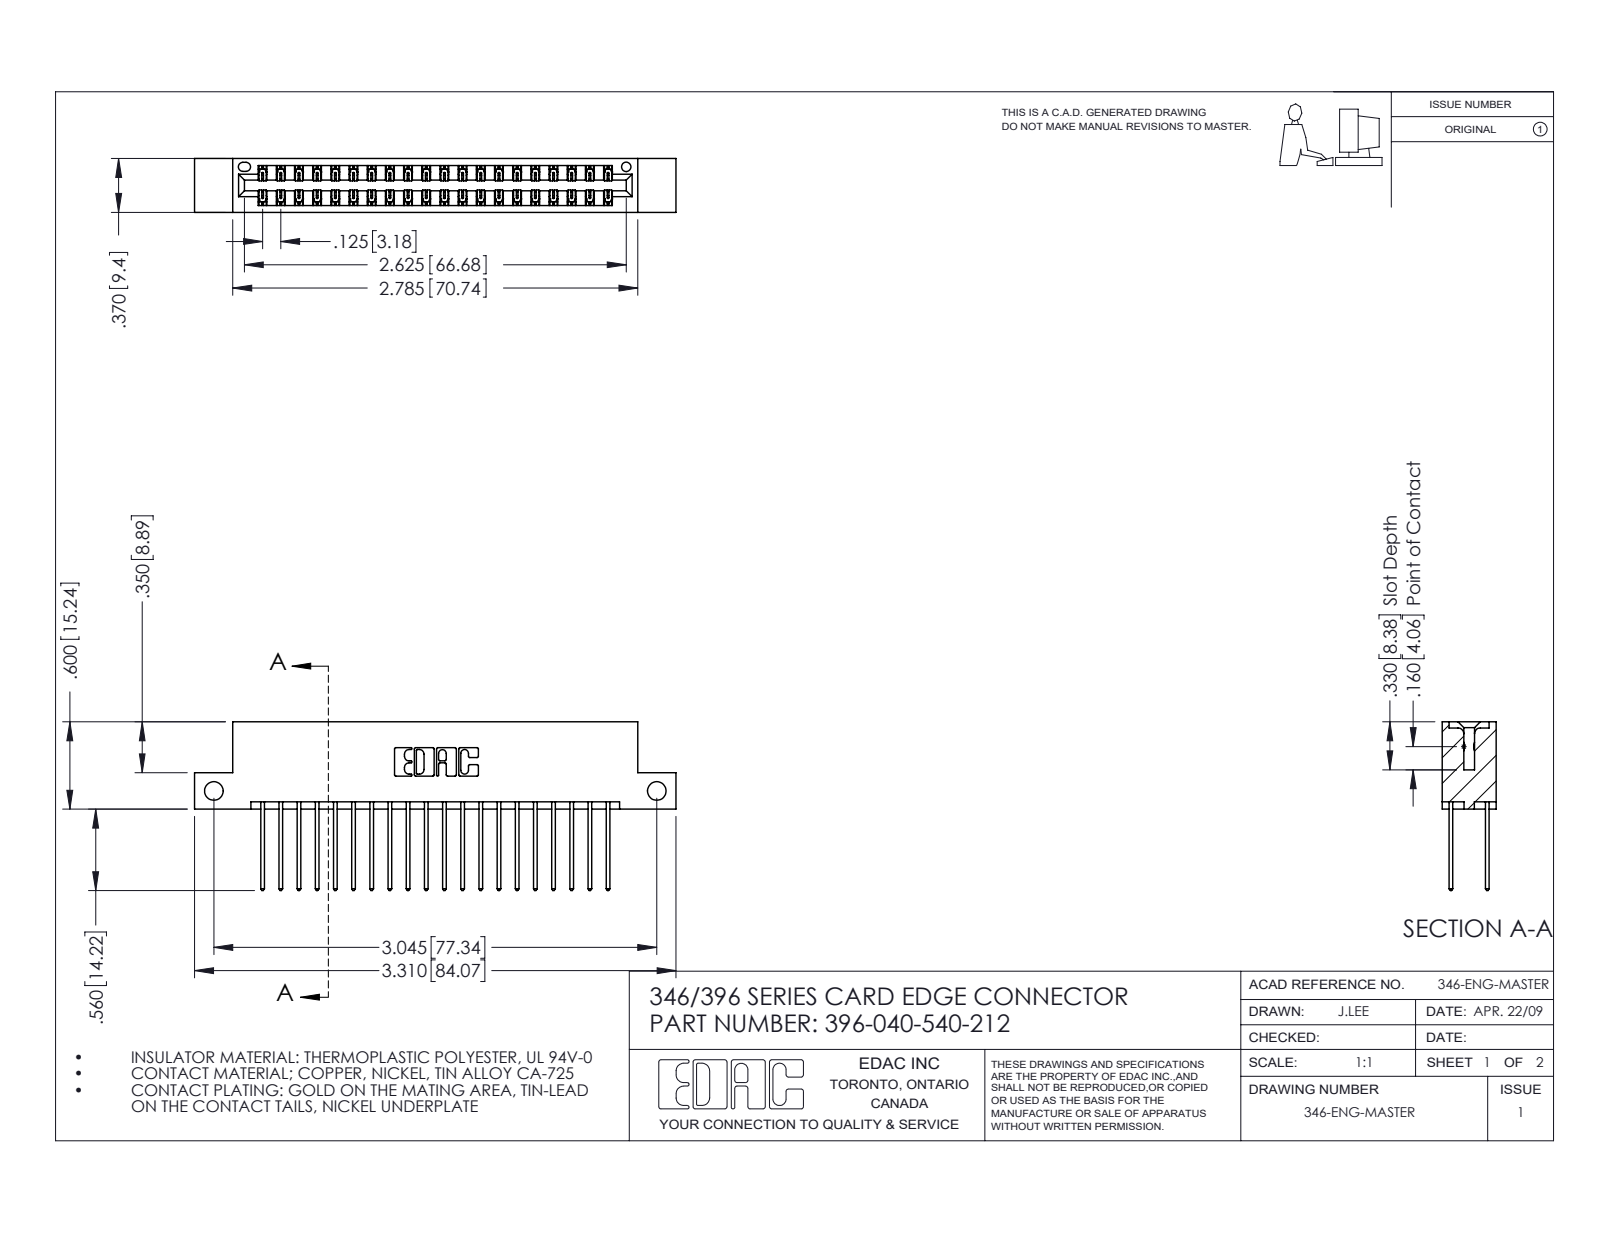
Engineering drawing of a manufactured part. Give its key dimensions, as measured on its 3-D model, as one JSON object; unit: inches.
{"part_name": "346 Part_Flush Mounting Lugs - Side Mount; 396-040-540-212; 345-292-001_345-293-140", "step_written_by": "SolidWorks 2016 (CONFIG_CONTROL_DESIGN)", "units": "inches", "bodies": {"solids": 41, "faces": 2202, "planar": 1476, "cylindrical": 726, "other": 0}, "overall_size": [3.31, 1.16, 0.37], "volume_in3": 0.494, "surface_area_in2": 17.6, "round_holes": [[0.128, 2], [0.064, 1]], "partial_cylinders_radius": [[0.006, 60], [0.01, 40], [0.01, 22], [0.007, 6], [0.031, 6], [0.026, 3], [0.014, 2], [0.022, 2]], "face_to_face_distances": [0.048, 0.322, 0.25, 0.072, 0.298, 0.025, 0.37, 0.275, 0.148, 0.222], "hole_center_spacings": [3.045]}
